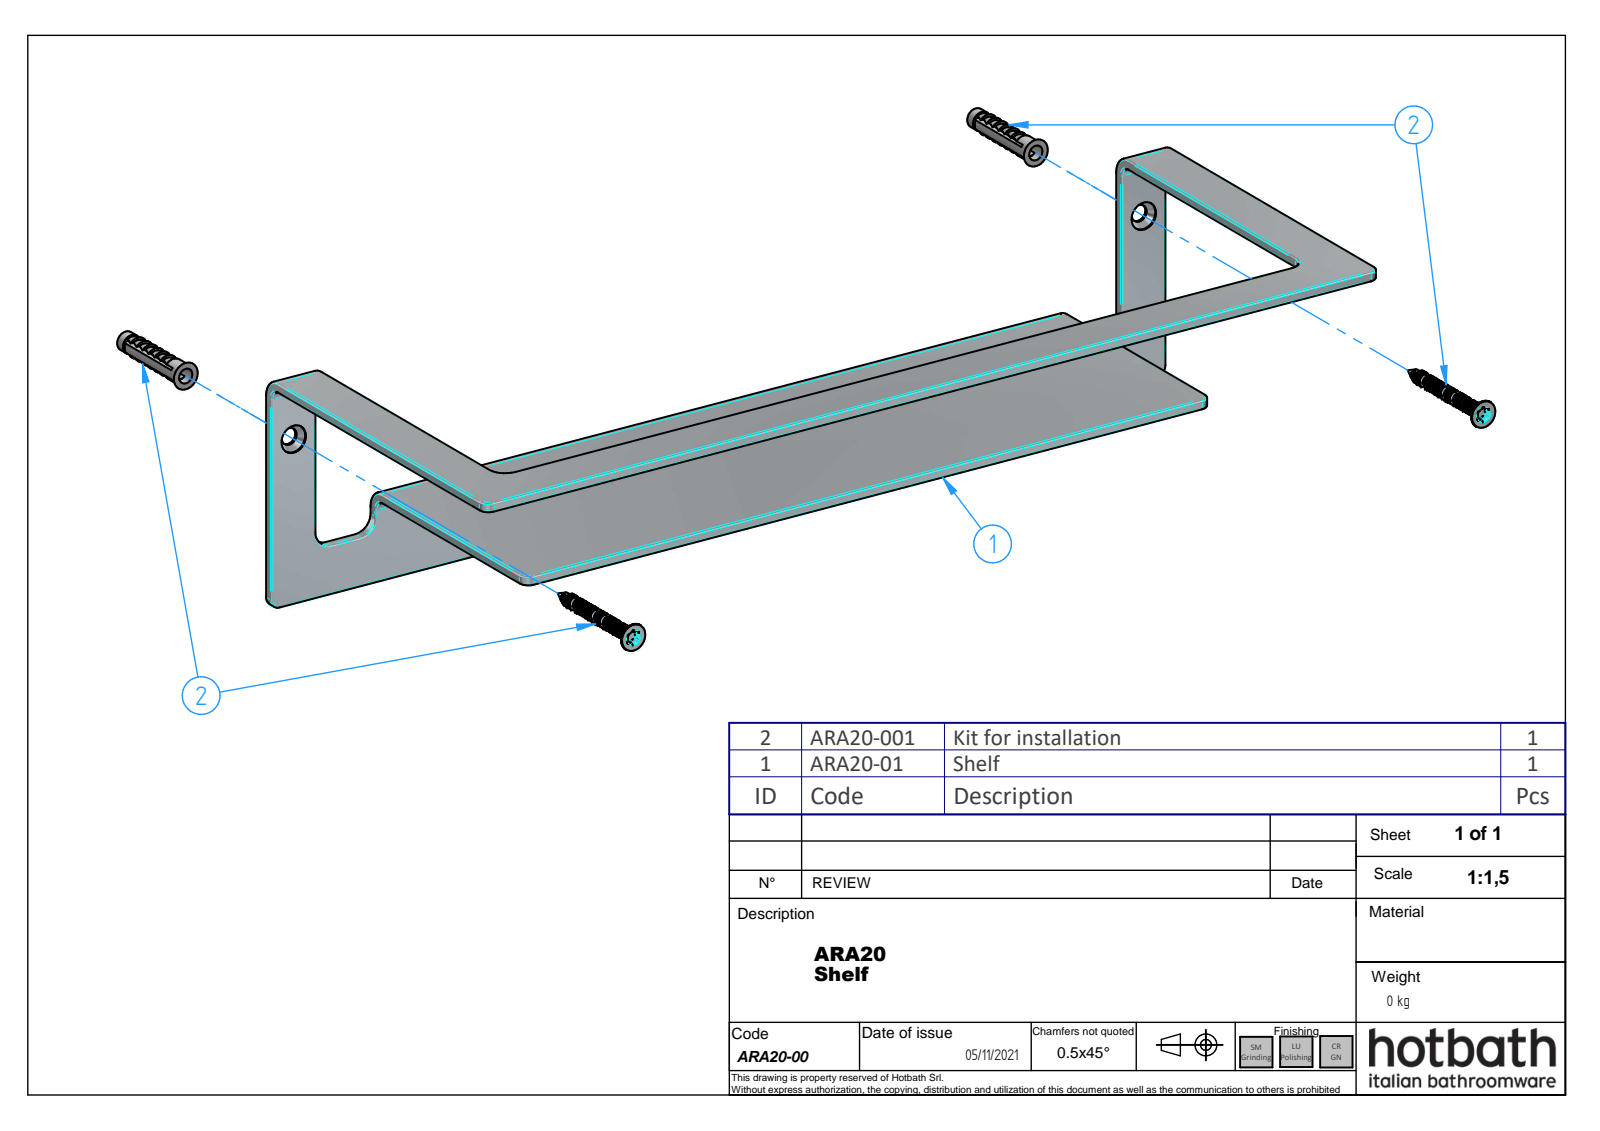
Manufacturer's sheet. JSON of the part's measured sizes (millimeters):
{"part_name": "ARA20-00; ARA20-01; ARA20-001_oa_0; C092090", "step_written_by": "ST-DEVELOPER v16.7 (AP242_MANAGED_MODEL_BASED_3D_ENGINEERING_MIM_LF)", "units": "millimeters", "bodies": {"solids": 3, "faces": 390, "planar": 48, "cylindrical": 150, "other": 192}, "overall_size": [300, 145, 69.79], "volume_mm3": 99524, "surface_area_mm2": 72531, "round_holes": [[5, 2], [8.2, 2]], "round_bosses_or_shafts": [[8, 2], [3.05, 2]], "partial_cylinders_radius": [[0.5, 34], [0.1, 24], [0.3, 12], [0.8, 12], [3, 8], [5, 6], [6, 2]], "face_to_face_distances": [3, 41.79, 44.79, 38.79, 15, 107, 110, 25, 28, 66.79], "hole_center_spacings": [285]}
